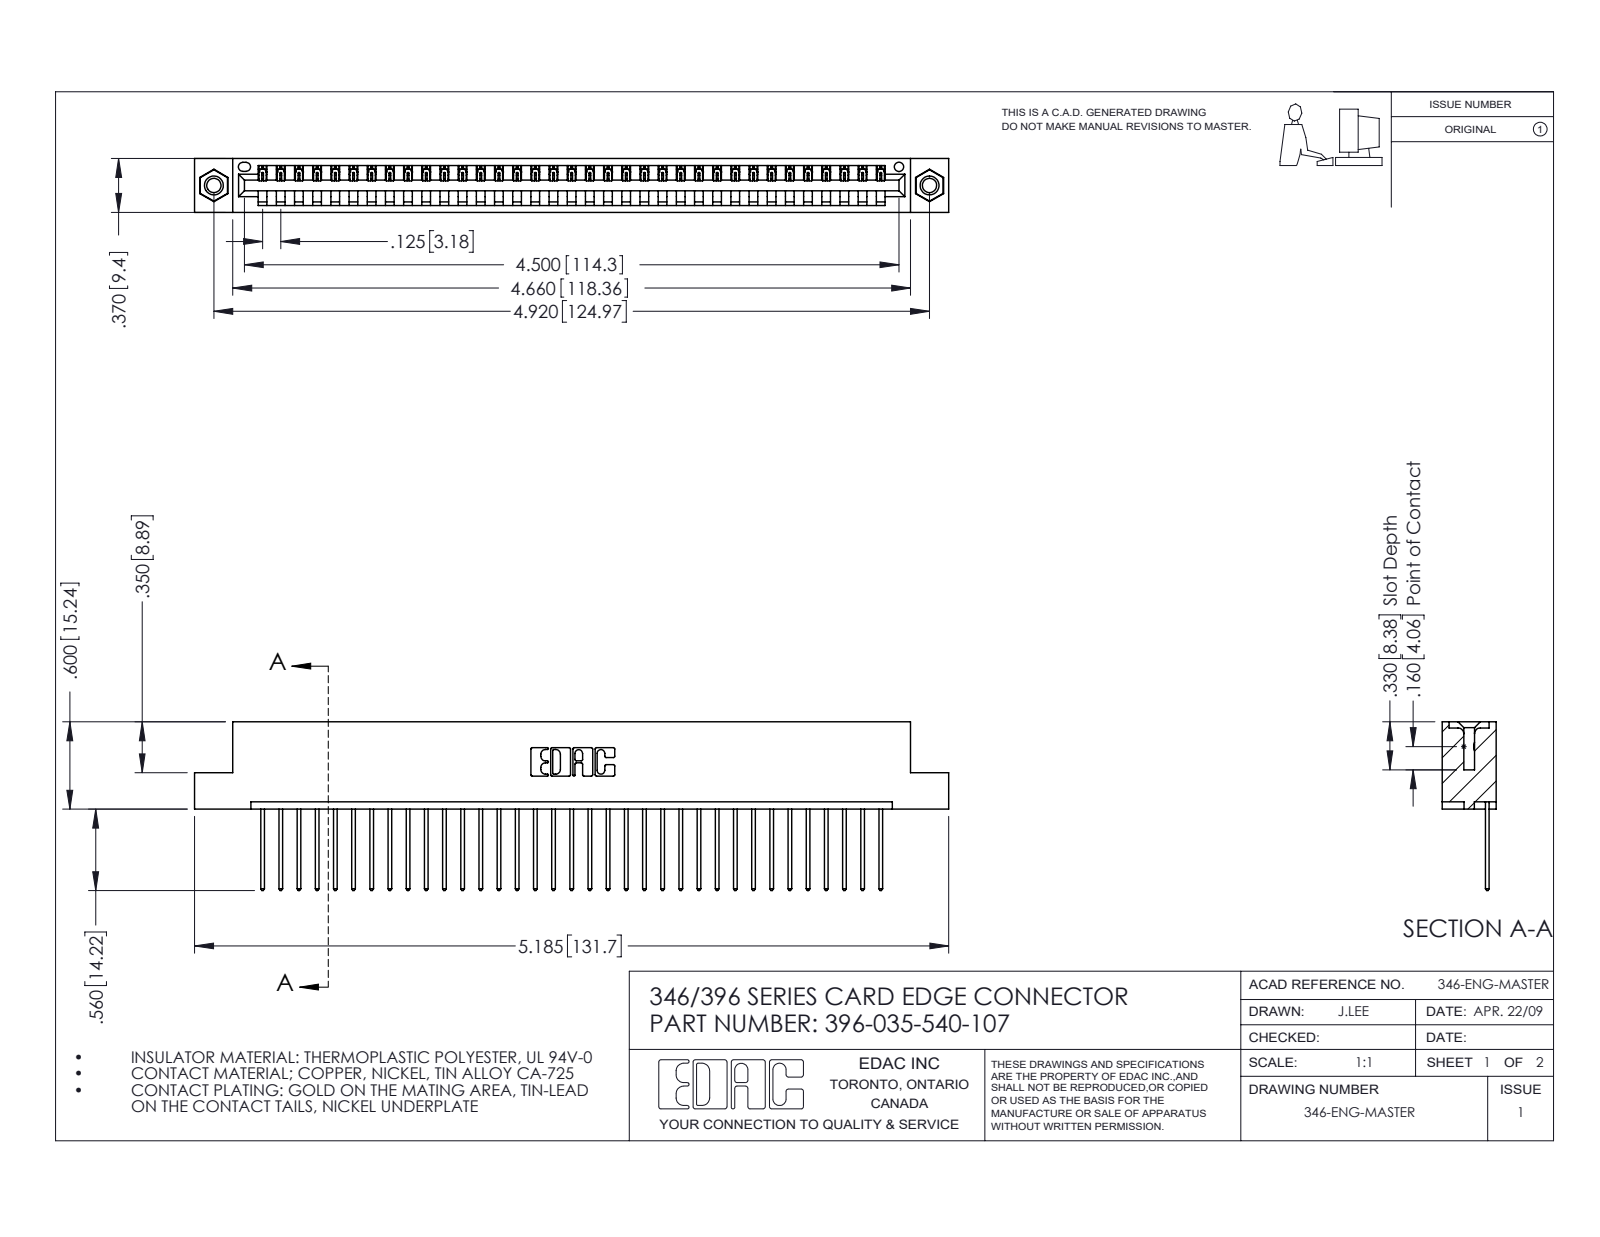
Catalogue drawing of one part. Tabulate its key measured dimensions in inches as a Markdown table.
| quantity | value |
| --- | --- |
| part name | 346 Part_Flush Mounting Lugs - 0.156 Dia-TI; 345-292-001_345-293-140; 345-250-001_345-250-005-103; 396-035-540-107 |
| STEP written by | SolidWorks 2016 (CONFIG_CONTROL_DESIGN) |
| units | inches |
| bodies | 38 solids, 2212 faces (1508 planar, 688 cylindrical, 16 other) |
| overall size | 5.185 × 1.16 × 0.37 |
| volume | 0.768 in³ |
| surface area | 24.87 in² |
| round holes (diameter × count) | 0.098 × 2, 0.125 × 2, 0.156 × 2, 0.064 × 1 |
| round bosses / shafts (diameter × count) | 0.155 × 2 |
| partial cylindrical surfaces (radius × count) | 0.006 × 70, 0.01 × 70, 0.01 × 22, 0.007 × 6, 0.031 × 6, 0.026 × 3, 0.031 × 2, 0.04 × 2 |
| main face-to-face distances | 0.048, 0.322, 0.37, 0.25, 0.072, 0.298, 0.025, 0.148, 0.222, 0.1 |
| hole center spacings | 0.246, 4.711, 4.92 |
